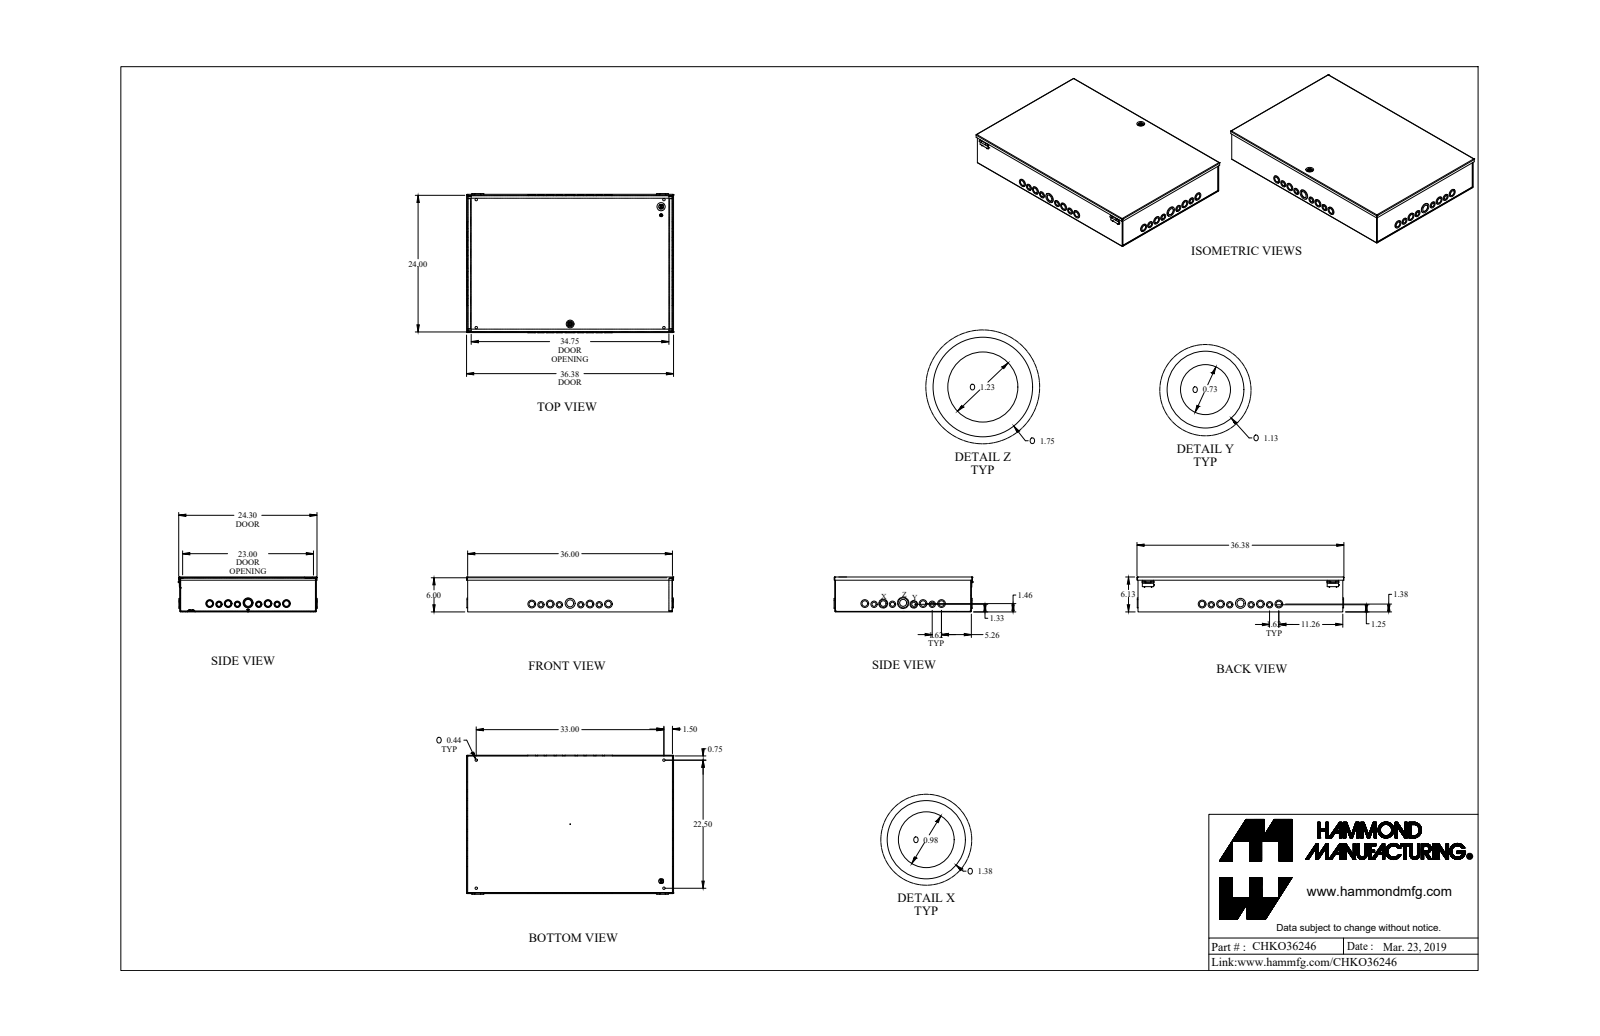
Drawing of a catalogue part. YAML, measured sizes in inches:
part_name: "CHKO36246_Default"
step_written_by: "SolidWorks 2019 (CONFIG_CONTROL_DESIGN)"
units: inches
bodies: {solids: 12, faces: 919, planar: 416, cylindrical: 460, other: 43}
overall_size: [36.375, 24.446, 6.133]
volume: 189.5
surface_area: 5294
round_holes:
  - {diameter: 0.981, count: 16}
  - {diameter: 1.231, count: 10}
  - {diameter: 0.731, count: 8}
  - {diameter: 0.437, count: 4}
  - {diameter: 1.606, count: 2}
  - {diameter: 0.125, count: 1}
  - {diameter: 0.17, count: 1}
  - {diameter: 0.319, count: 1}
  - {diameter: 0.476, count: 1}
  - {diameter: 0.5, count: 1}
round_bosses_or_shafts:
  - {diameter: 1.125, count: 14}
  - {diameter: 1.375, count: 9}
  - {diameter: 0.131, count: 8}
  - {diameter: 0.875, count: 6}
  - {diameter: 0.875, count: 6}
  - {diameter: 1.125, count: 4}
  - {diameter: 1.375, count: 3}
  - {diameter: 1.75, count: 2}
partial_cylinders:
  - {radius: 0.036, count: 18}
  - {radius: 0.108, count: 16}
  - {radius: 0.072, count: 8}
  - {radius: 0.012, count: 4}
  - {radius: 0.1, count: 4}
  - {radius: 0.079, count: 2}
  - {radius: 0.25, count: 2}
  - {radius: 0.022, count: 1}
face_to_face_distances: [0.072, 6.061, 6.133, 5.989, 23.928, 35.928, 24, 23.856, 36, 35.856]
hole_center_spacings: [1.625, 3.24, 8.621, 7, 10.24, 1.896, 3.502, 4.862]
